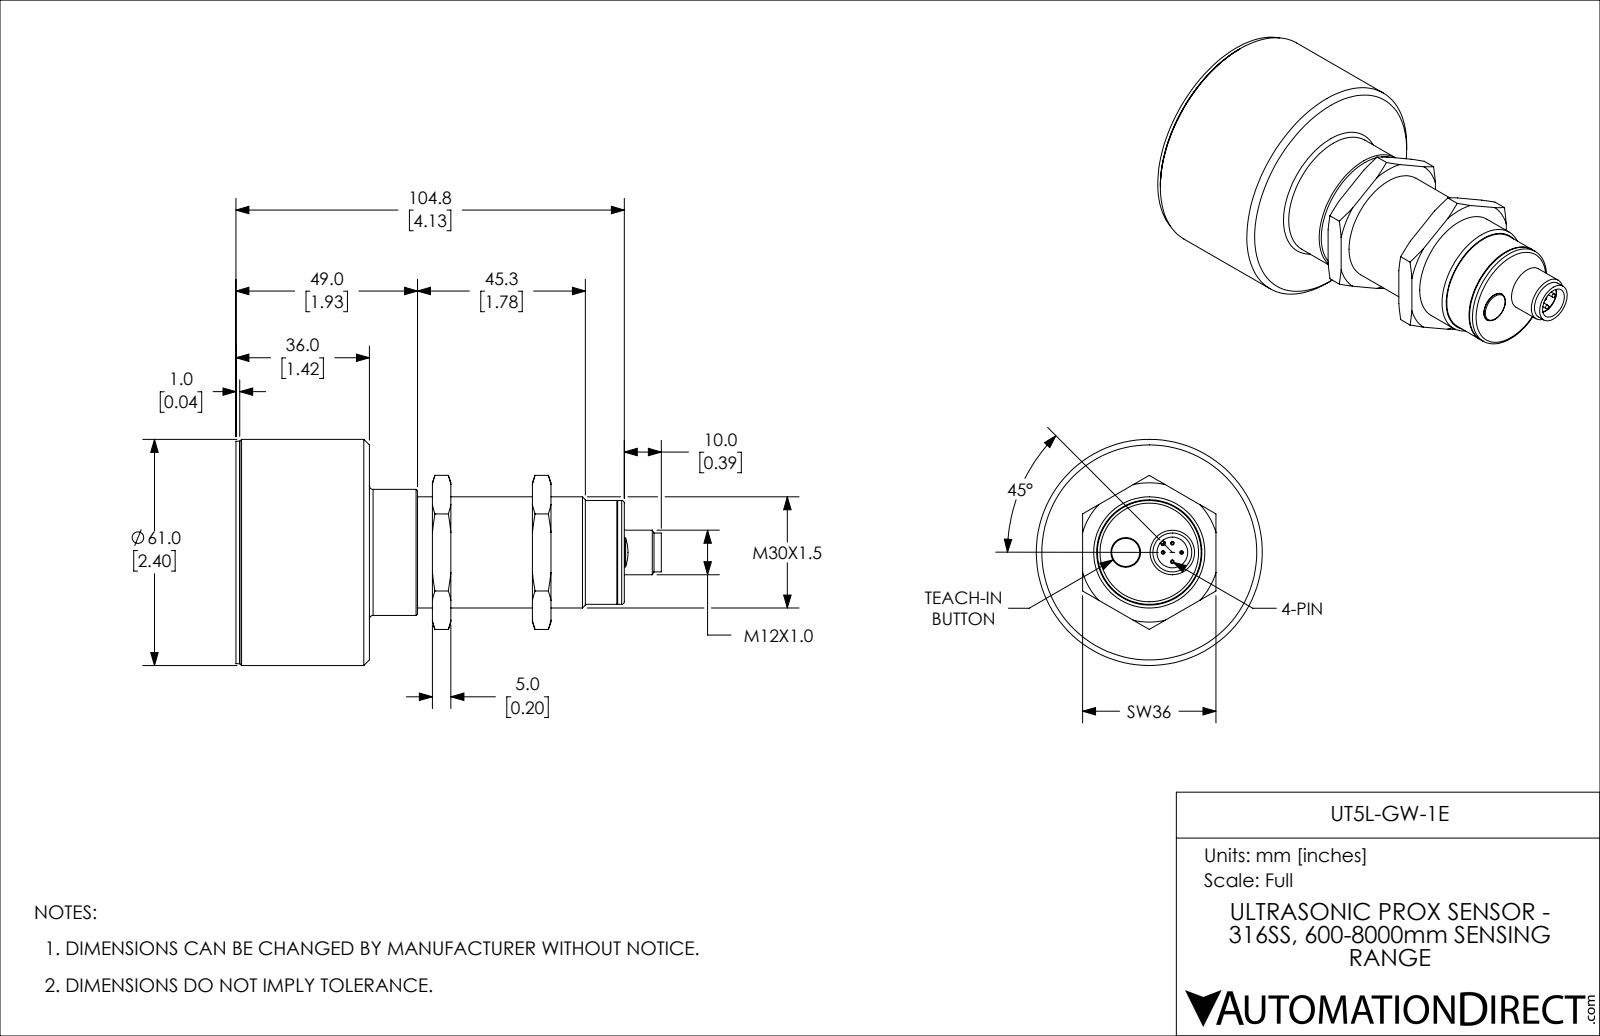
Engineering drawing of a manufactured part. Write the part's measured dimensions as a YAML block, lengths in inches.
part_name: "UT5L-GW-1E"
step_written_by: "SolidWorks 2018 (AUTOMOTIVE_DESIGN)"
units: inches
bodies: {solids: 9, faces: 180, planar: 52, cylindrical: 57, other: 71}
overall_size: [4.52, 2.402, 2.402]
volume: 11.87
surface_area: 55.78
round_holes:
  - {diameter: 0.071, count: 4}
  - {diameter: 0.315, count: 1}
  - {diameter: 0.327, count: 1}
  - {diameter: 0.372, count: 1}
  - {diameter: 1.181, count: 1}
  - {diameter: 1.969, count: 1}
round_bosses_or_shafts:
  - {diameter: 0.039, count: 4}
  - {diameter: 2.402, count: 1}
  - {diameter: 2.362, count: 1}
  - {diameter: 1.339, count: 1}
  - {diameter: 1.114, count: 1}
  - {diameter: 1.102, count: 1}
  - {diameter: 0.472, count: 1}
  - {diameter: 0.413, count: 1}
partial_cylinders:
  - {radius: 0.012, count: 2}
  - {radius: 0.024, count: 1}
face_to_face_distances: [1.417, 1.378, 0.039, 0.512, 0.866, 0.551, 1.929, 2.638, 4.055, 4.016]
hole_center_spacings: [0.098, 0.139, 0.197, 0.264, 0.505, 0.139, 0.146, 0.245]
